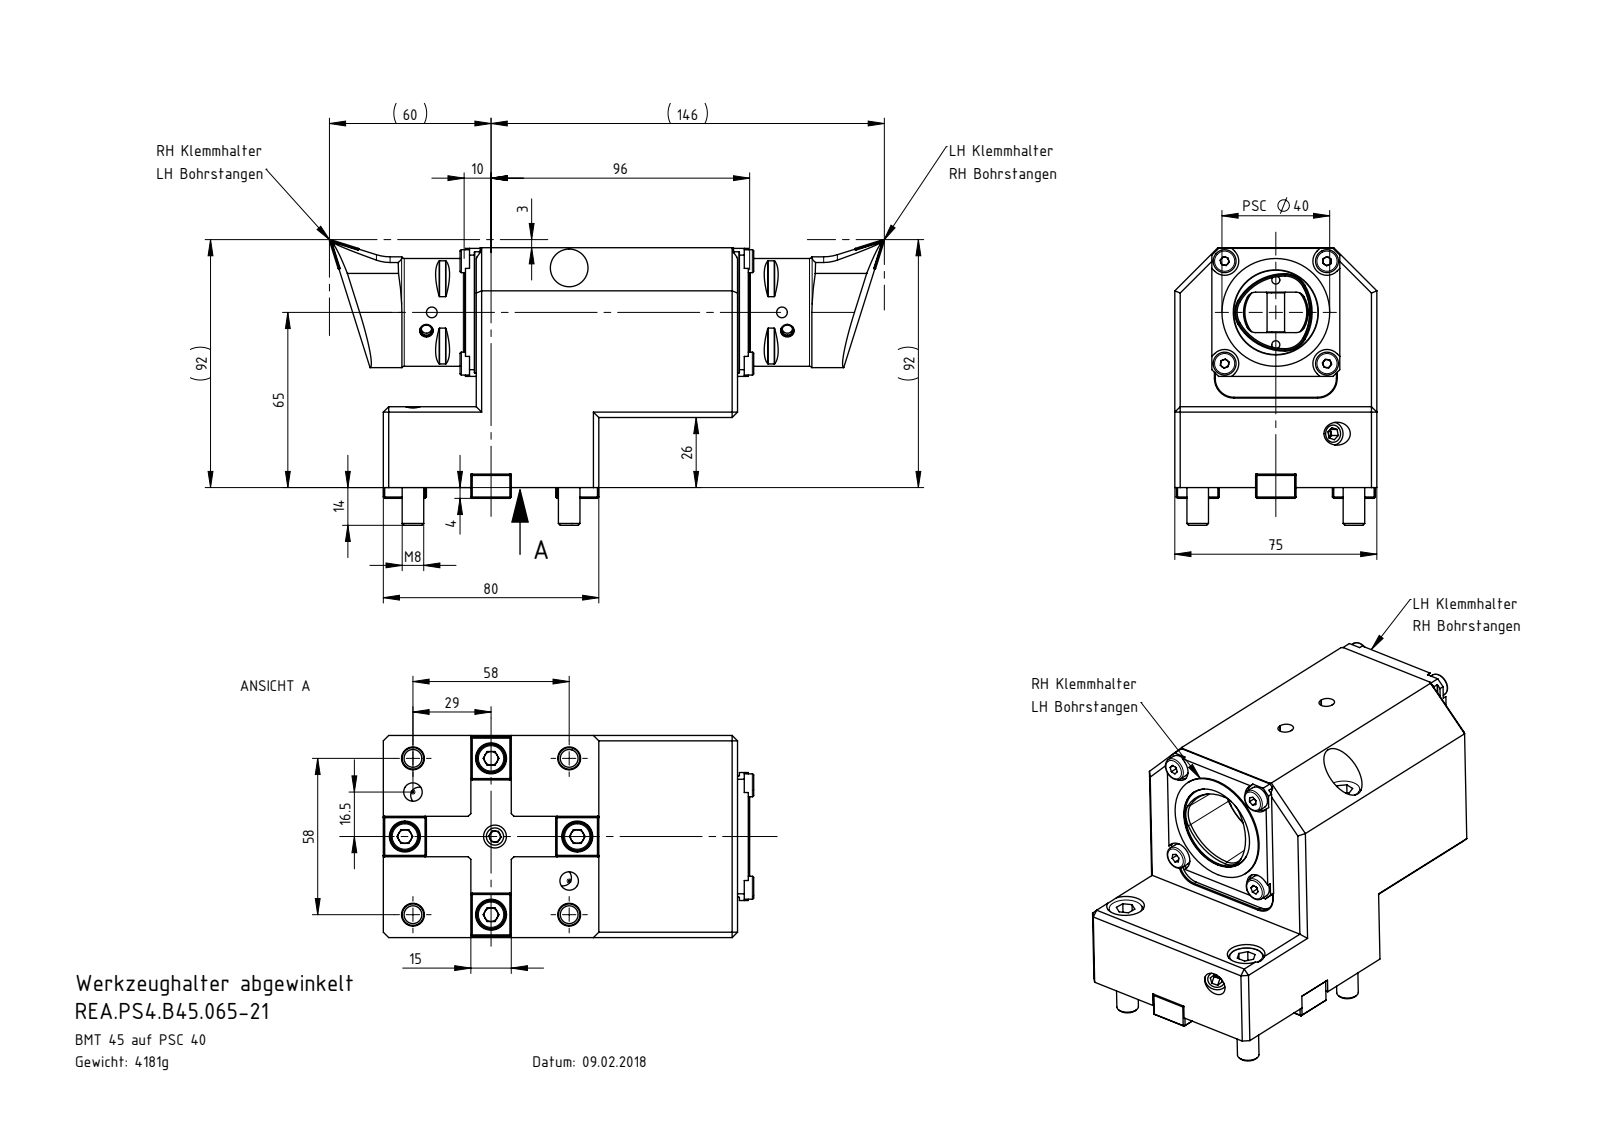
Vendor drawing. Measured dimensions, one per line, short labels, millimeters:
name: DIN 6325_ø2.5x8_2x6; U40-PS4.023.006_D; BM5-ER1.015.009_A; REA.PS4.B45.065-21 (+8 more)
written by: SolidWorks 2017 (AUTOMOTIVE_DESIGN)
unit: mm
bodies: 49 solids, 1340 faces (808 planar, 208 cylindrical, 324 other)
size: 137.5 × 103 × 75
volume: 544 887 mm³; area: 136 174 mm²
holes: 6× ⌀2.5, 6× ⌀4, 6× ⌀6.8, 6× ⌀8.5, 4× ⌀3.3, 4× ⌀4.2, 4× ⌀5, 4× ⌀5.5, 4× ⌀6.5, 4× ⌀11, 4× ⌀14, 2× ⌀3
bosses: 10× ⌀8, 4× ⌀13, 4× ⌀10, 4× ⌀8.5, 4× ⌀6, 4× ⌀5.5, 4× ⌀5, 4× ⌀3
rounds: 4× R0.2, 4× R2.75, 4× R3, 4× R3.5, 4× R5.25, 2× R7, 2× R9, 1× R12
face distances: 75, 30, 4, 89, 26, 63, 5, 47.5, 1.5, 2
hole spacings: 29.15, 58, 12.69, 15.77, 16.49, 20.25, 24.15, 26.28
